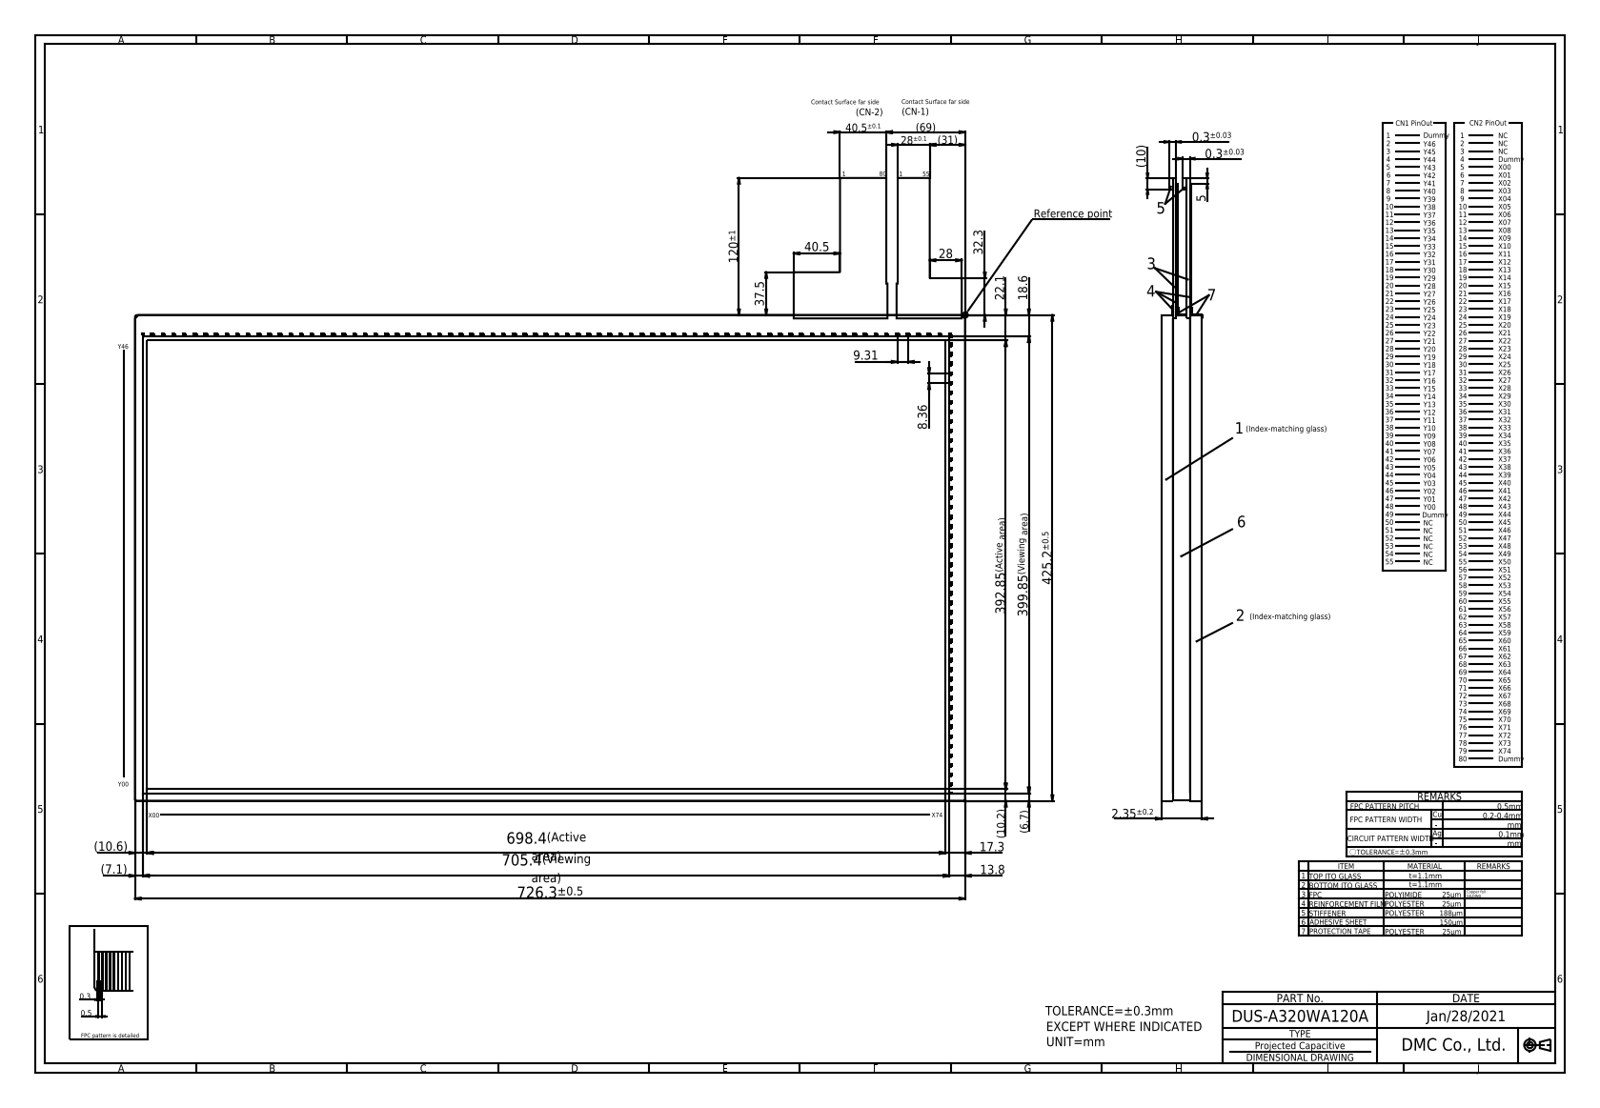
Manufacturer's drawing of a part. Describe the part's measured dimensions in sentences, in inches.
The part is named "DUS-A320WA120A". Its 3-D file was written by "Autodesk Inventor 2020 (CONFIG_CONTROL_DESIGN)". It is 1 solid with 594 faces: 586 planar, 8 cylindrical and 0 other. Overall it measures 40.032 by 24.813 by 0.093 inches. Its volume is 44.31 cubic inches and its surface area 999.7 square inches. Partial cylindrical surfaces (rounded edges, fillets, slot ends): 8 of radius 0.02. The main face-to-face distances are 0.093, 0.043, 0.045, 0.047, 0.049, 0.039, 0.089, 16.741, 28.594, 0.031.
